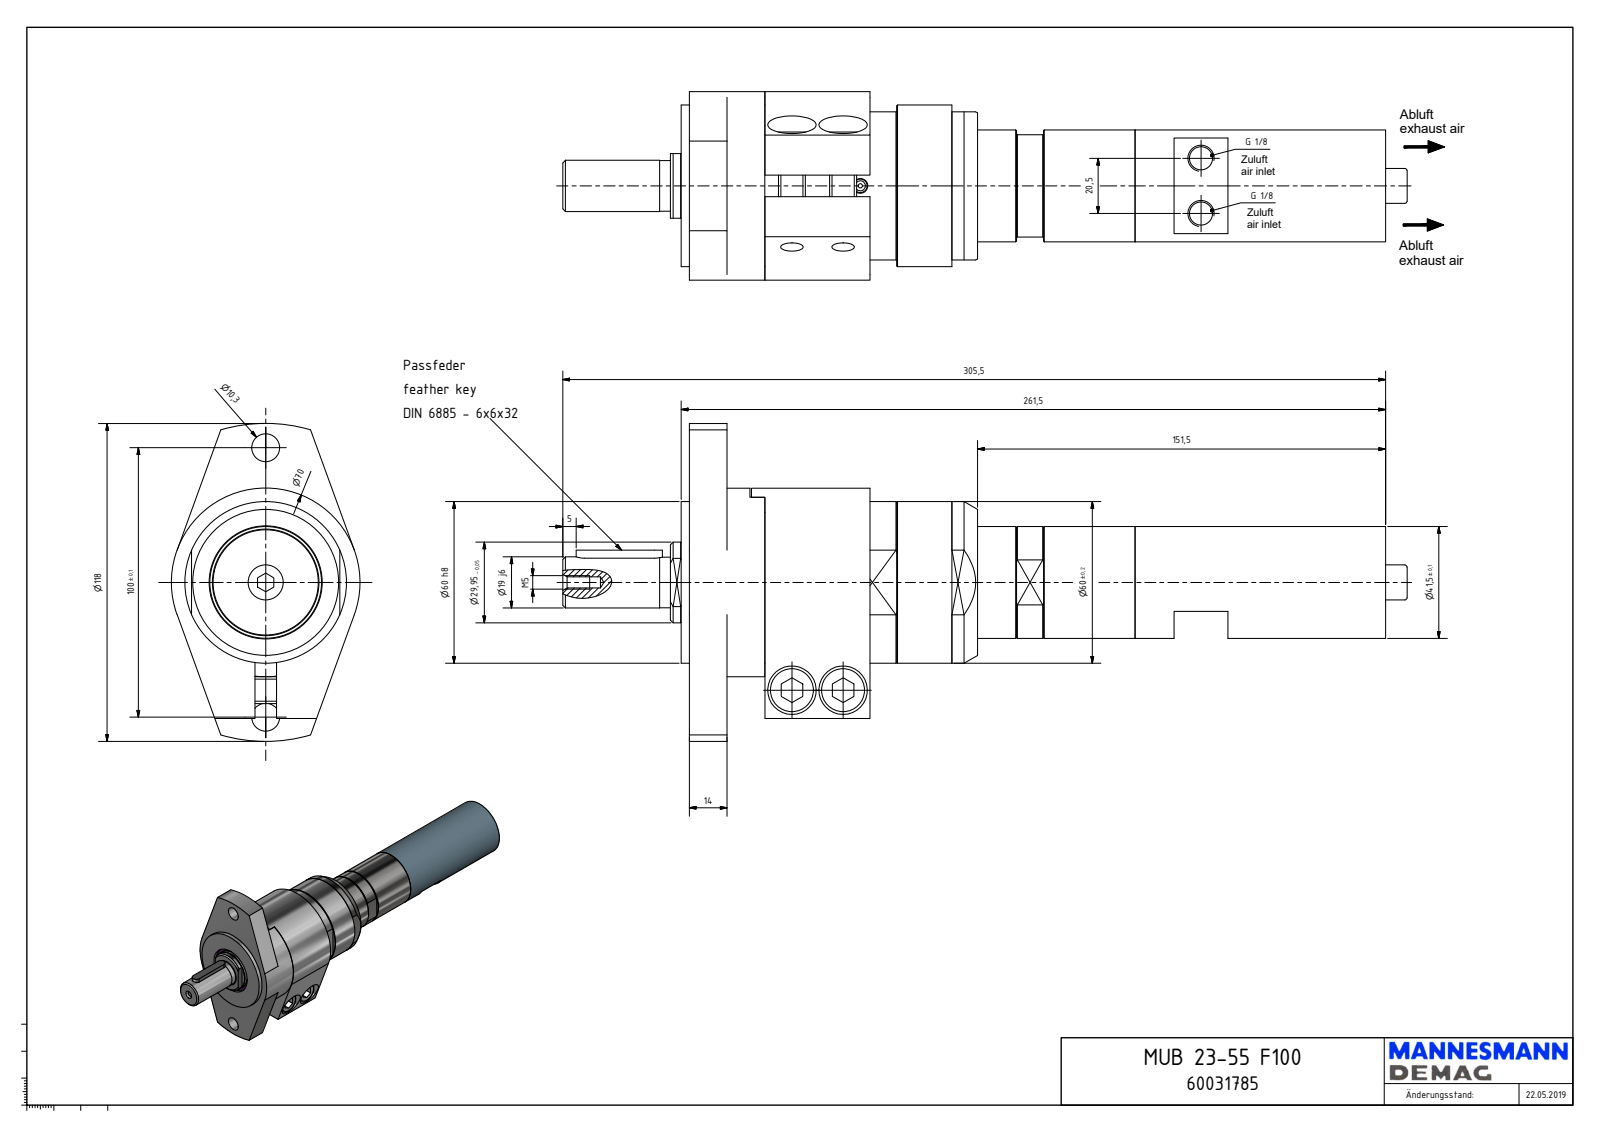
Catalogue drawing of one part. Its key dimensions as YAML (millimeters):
part_name: "MUB 23-55 F100_60031785"
step_written_by: "Autodesk Inventor 2018 (AUTOMOTIVE_DESIGN)"
units: millimeters
bodies: {solids: 1, faces: 227, planar: 113, cylindrical: 75, other: 39}
overall_size: [313.5, 118, 70]
volume: 644332
surface_area: 76961
round_holes:
  - {diameter: 8.38, count: 2}
  - {diameter: 8.57, count: 2}
  - {diameter: 10.3, count: 2}
  - {diameter: 10.5, count: 2}
  - {diameter: 18, count: 2}
  - {diameter: 1.55, count: 1}
  - {diameter: 4, count: 1}
  - {diameter: 4.13, count: 1}
  - {diameter: 5.5, count: 1}
  - {diameter: 8.5, count: 1}
  - {diameter: 35, count: 1}
  - {diameter: 39.5, count: 1}
round_bosses_or_shafts:
  - {diameter: 16, count: 2}
  - {diameter: 10, count: 2}
  - {diameter: 70, count: 1}
  - {diameter: 60, count: 1}
  - {diameter: 55.18, count: 1}
  - {diameter: 41.5, count: 1}
  - {diameter: 39, count: 1}
  - {diameter: 29.95, count: 1}
partial_cylinders:
  - {radius: 1.6, count: 2}
  - {radius: 2.5, count: 2}
  - {radius: 3, count: 2}
  - {radius: 14.65, count: 1}
  - {radius: 26.85, count: 1}
  - {radius: 27.76, count: 1}
  - {radius: 59, count: 1}
face_to_face_distances: [14, 17, 3, 70.1, 39, 67.1, 53.1, 31.1, 28.1, 14.1]
hole_center_spacings: [50, 126.91, 19, 20.5, 100]
